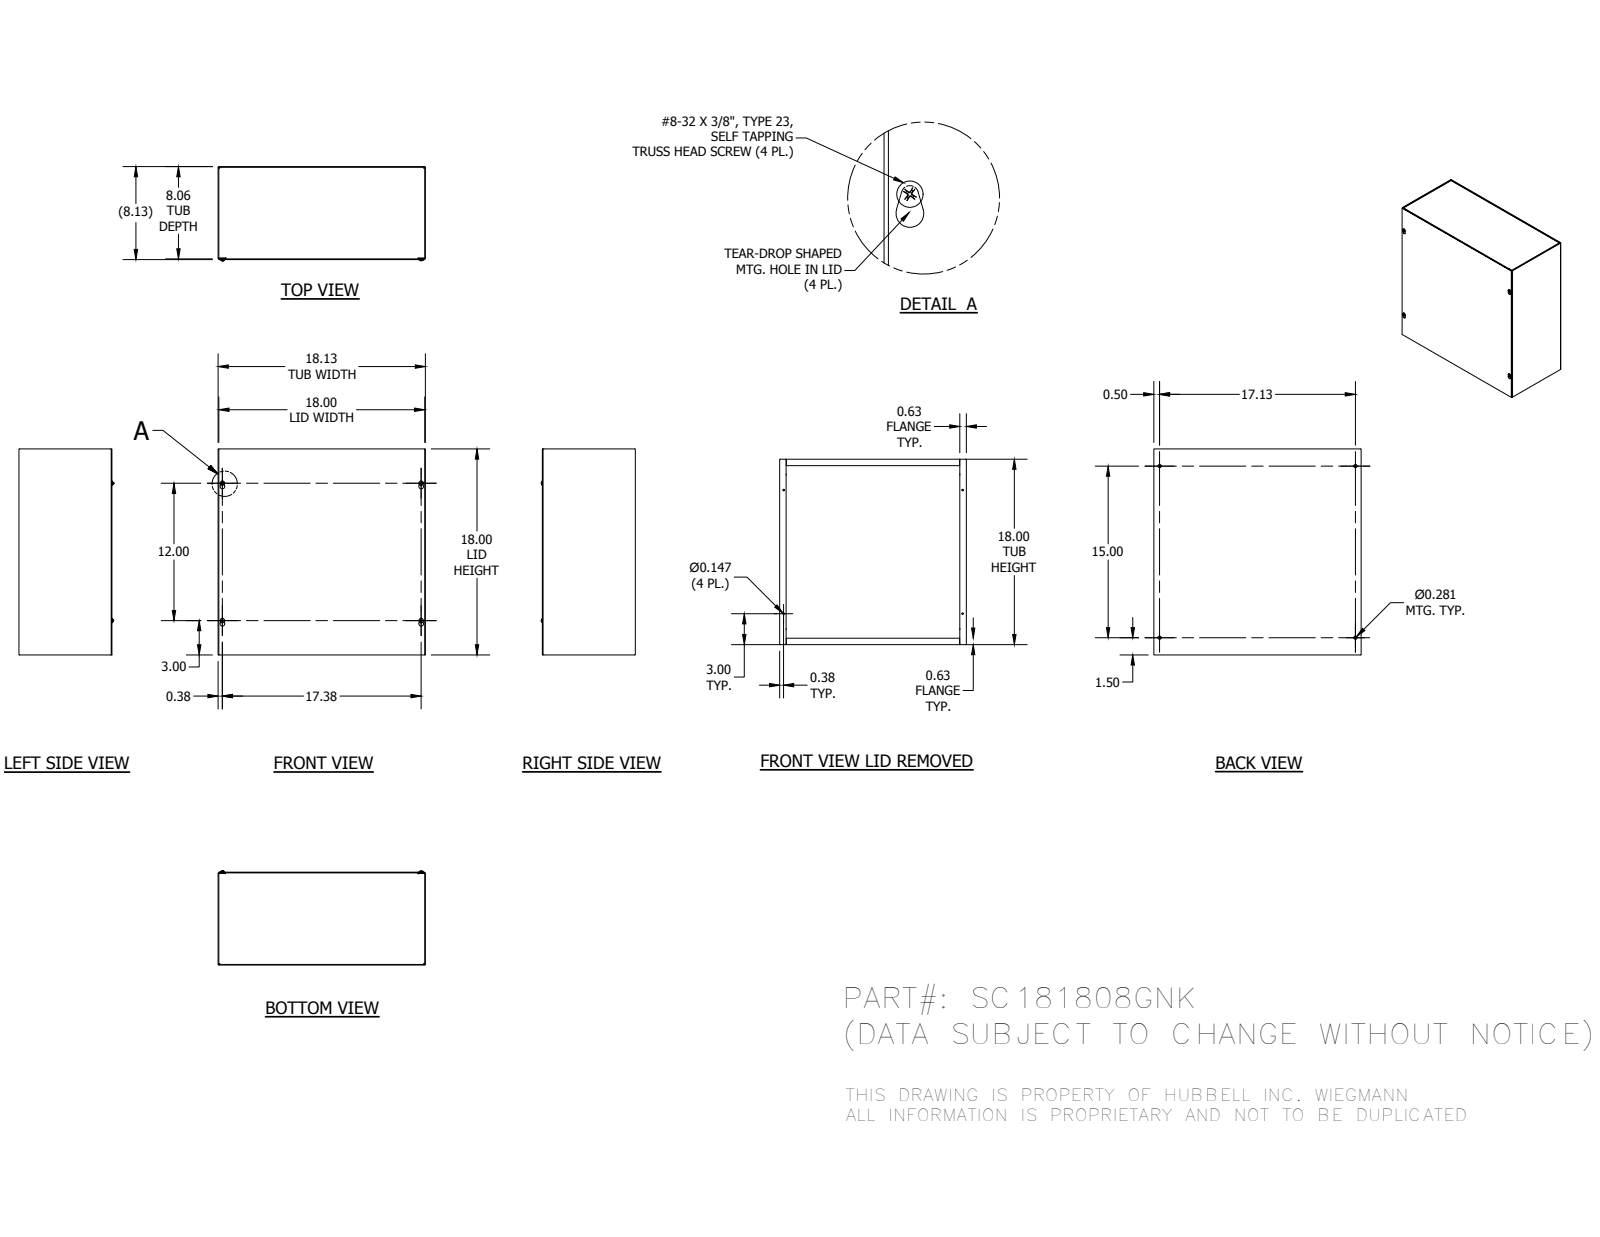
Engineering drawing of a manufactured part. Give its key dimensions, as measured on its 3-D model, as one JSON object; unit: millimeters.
{"part_name": "SC181808GNKBLR; SC1808GNKTB; SC1818GLPA; 34056 (+1 more)", "step_written_by": "Autodesk Inventor 2014 (AUTOMOTIVE_DESIGN)", "units": "millimeters", "bodies": {"solids": 8, "faces": 268, "planar": 152, "cylindrical": 48, "other": 68}, "overall_size": [460.38, 457.2, 208.92], "volume_mm3": 1331000, "surface_area_mm2": 1689000, "round_holes": [[3.73, 4], [7.14, 4]], "round_bosses_or_shafts": [[9.75, 4], [4.17, 4]], "partial_cylinders_radius": [[0.4, 12], [1.98, 12], [3.17, 4], [5.16, 4]], "face_to_face_distances": [1.59, 204.79, 203.2, 206.38, 457.2, 455.61, 458.79, 454.02, 460.38, 3.18], "hole_center_spacings": [38.23, 342.91, 439.8, 556.38, 304.8, 381, 434.98, 441.32]}
